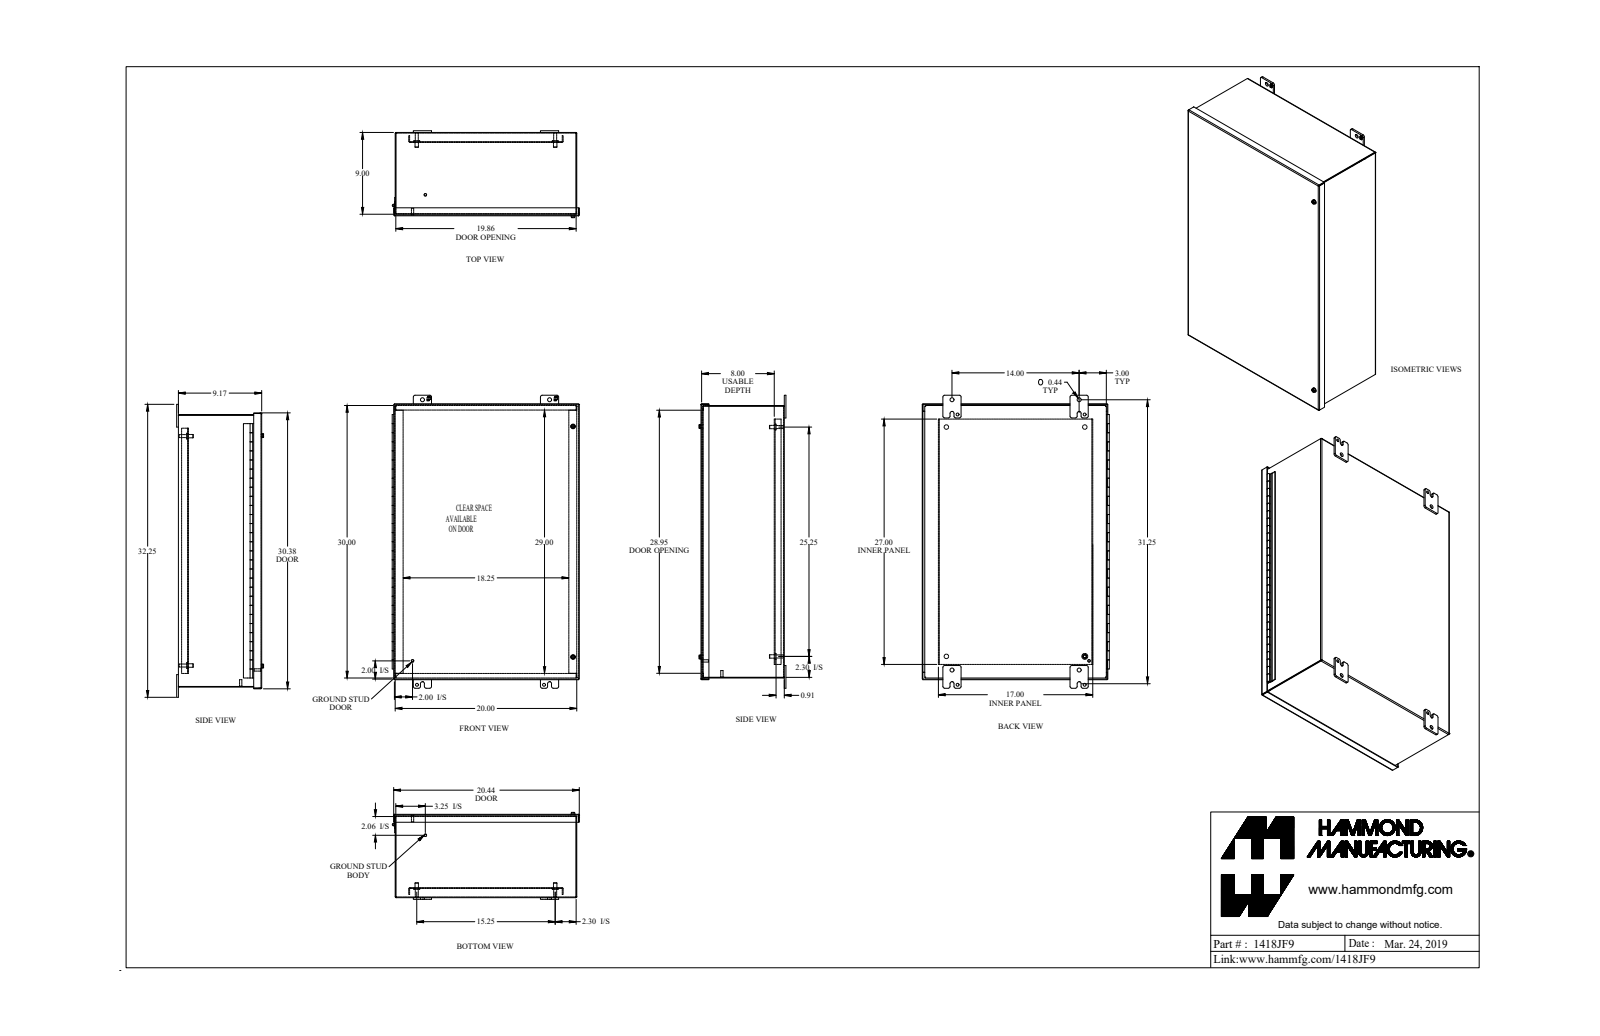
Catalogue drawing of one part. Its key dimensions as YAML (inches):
part_name: "1418JF9_Default"
step_written_by: "SolidWorks 2018 (CONFIG_CONTROL_DESIGN)"
units: inches
bodies: {solids: 32, faces: 978, planar: 599, cylindrical: 337, other: 42}
overall_size: [32.25, 20.604, 9.571]
volume: 244.4
surface_area: 6060
round_holes:
  - {diameter: 0.313, count: 6}
  - {diameter: 0.437, count: 4}
  - {diameter: 0.5, count: 4}
  - {diameter: 0.26, count: 2}
  - {diameter: 0.266, count: 2}
  - {diameter: 0.28, count: 2}
  - {diameter: 0.29, count: 2}
  - {diameter: 0.307, count: 2}
  - {diameter: 0.397, count: 2}
  - {diameter: 0.445, count: 2}
  - {diameter: 0.187, count: 1}
  - {diameter: 3.5, count: 1}
round_bosses_or_shafts:
  - {diameter: 0.65, count: 4}
  - {diameter: 0.375, count: 4}
  - {diameter: 0.33, count: 4}
  - {diameter: 1, count: 2}
  - {diameter: 0.51, count: 2}
  - {diameter: 0.5, count: 2}
  - {diameter: 0.39, count: 2}
  - {diameter: 0.281, count: 2}
partial_cylinders:
  - {radius: 0.188, count: 24}
  - {radius: 0.25, count: 20}
  - {radius: 0.036, count: 12}
  - {radius: 0.108, count: 12}
  - {radius: 0.218, count: 8}
  - {radius: 0.133, count: 6}
  - {radius: 0.06, count: 5}
  - {radius: 0.125, count: 4}
face_to_face_distances: [0.072, 9.1, 9.172, 9.028, 19.928, 0.095, 7.996, 8.091, 1.104, 1.032]
hole_center_spacings: [29.498, 1.736, 14, 15.25, 29.75, 32.88, 1.907, 1.966]
